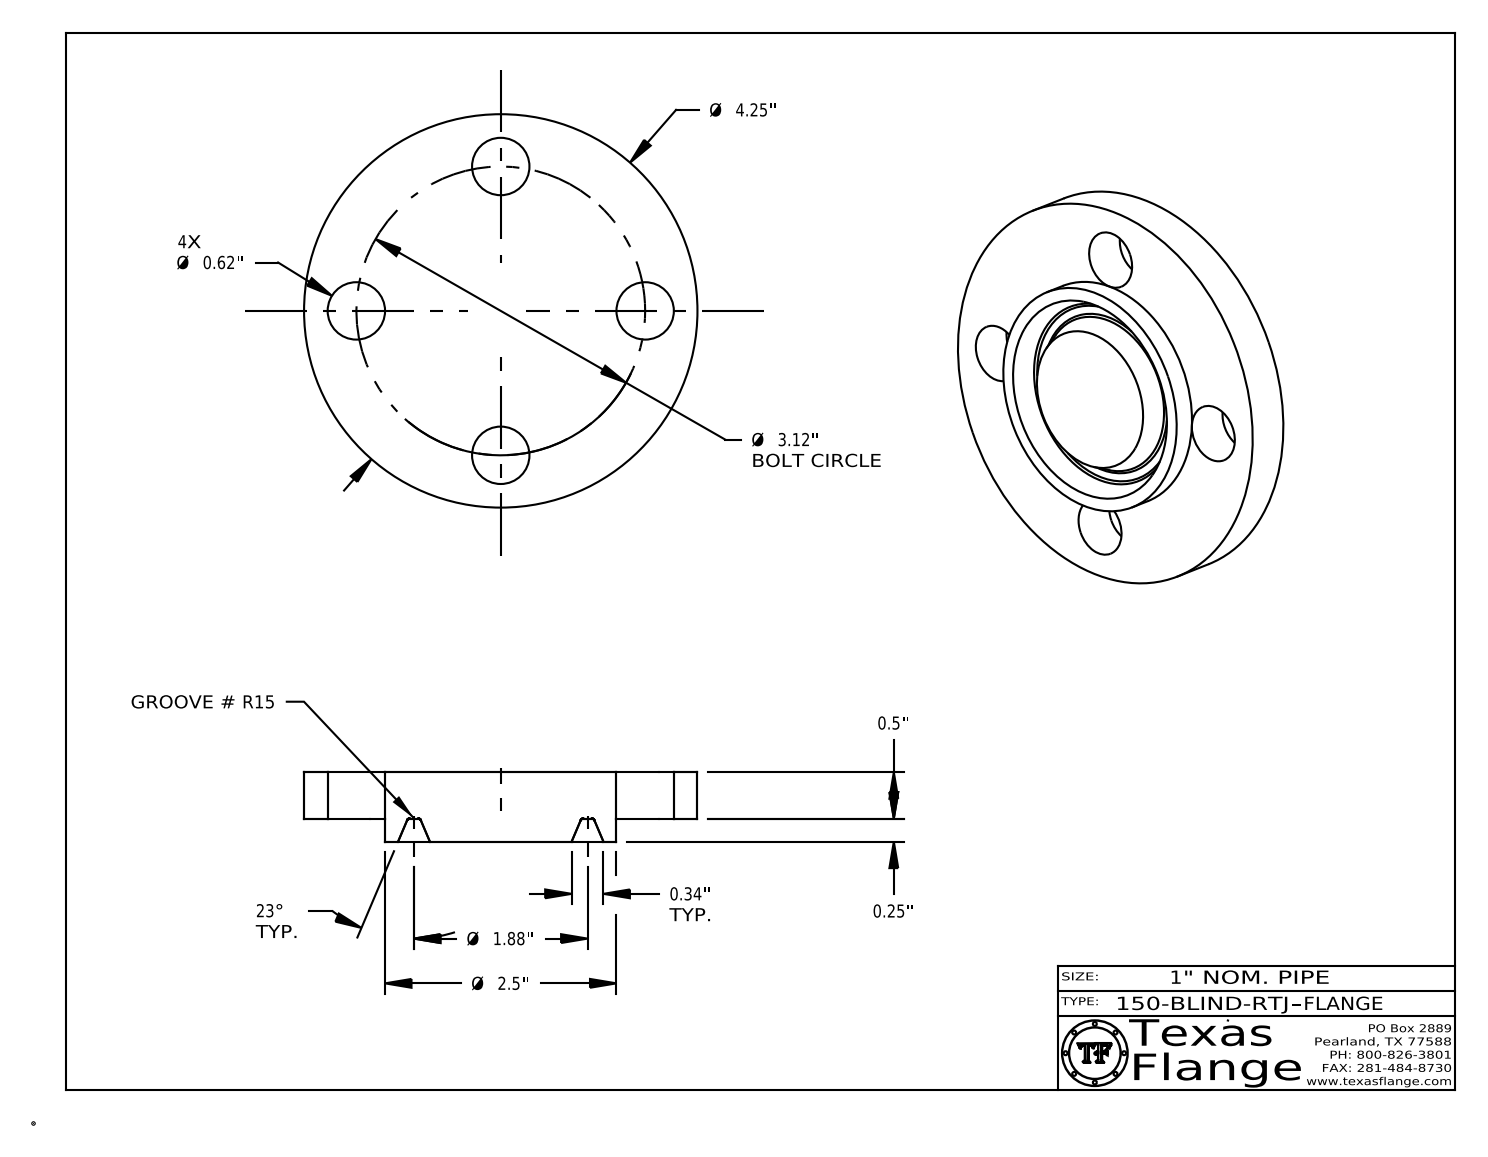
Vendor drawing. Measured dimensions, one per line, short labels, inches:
name: 150-BLIND-RTJ
written by: CATIA V5 STEP AP214 (AUTOMOTIVE_DESIGN)
unit: in
bodies: 1 solid, 410 faces (370 planar, 32 cylindrical, 8 other)
size: 4.25 × 4.25 × 0.75
volume: 7.366 in³; area: 40.48 in²
holes: 4× ⌀0.62, 1× ⌀0.495
bosses: 8× ⌀0.03, 1× ⌀4.25, 1× ⌀2.5, 1× ⌀0.39
face distances: 0.5, 0.25, 0.75, 0.735, 0.485, 0.015, 0.148, 0.144, 0.027, 0.096
hole spacings: 2.206, 1.194, 2.882, 3.12
